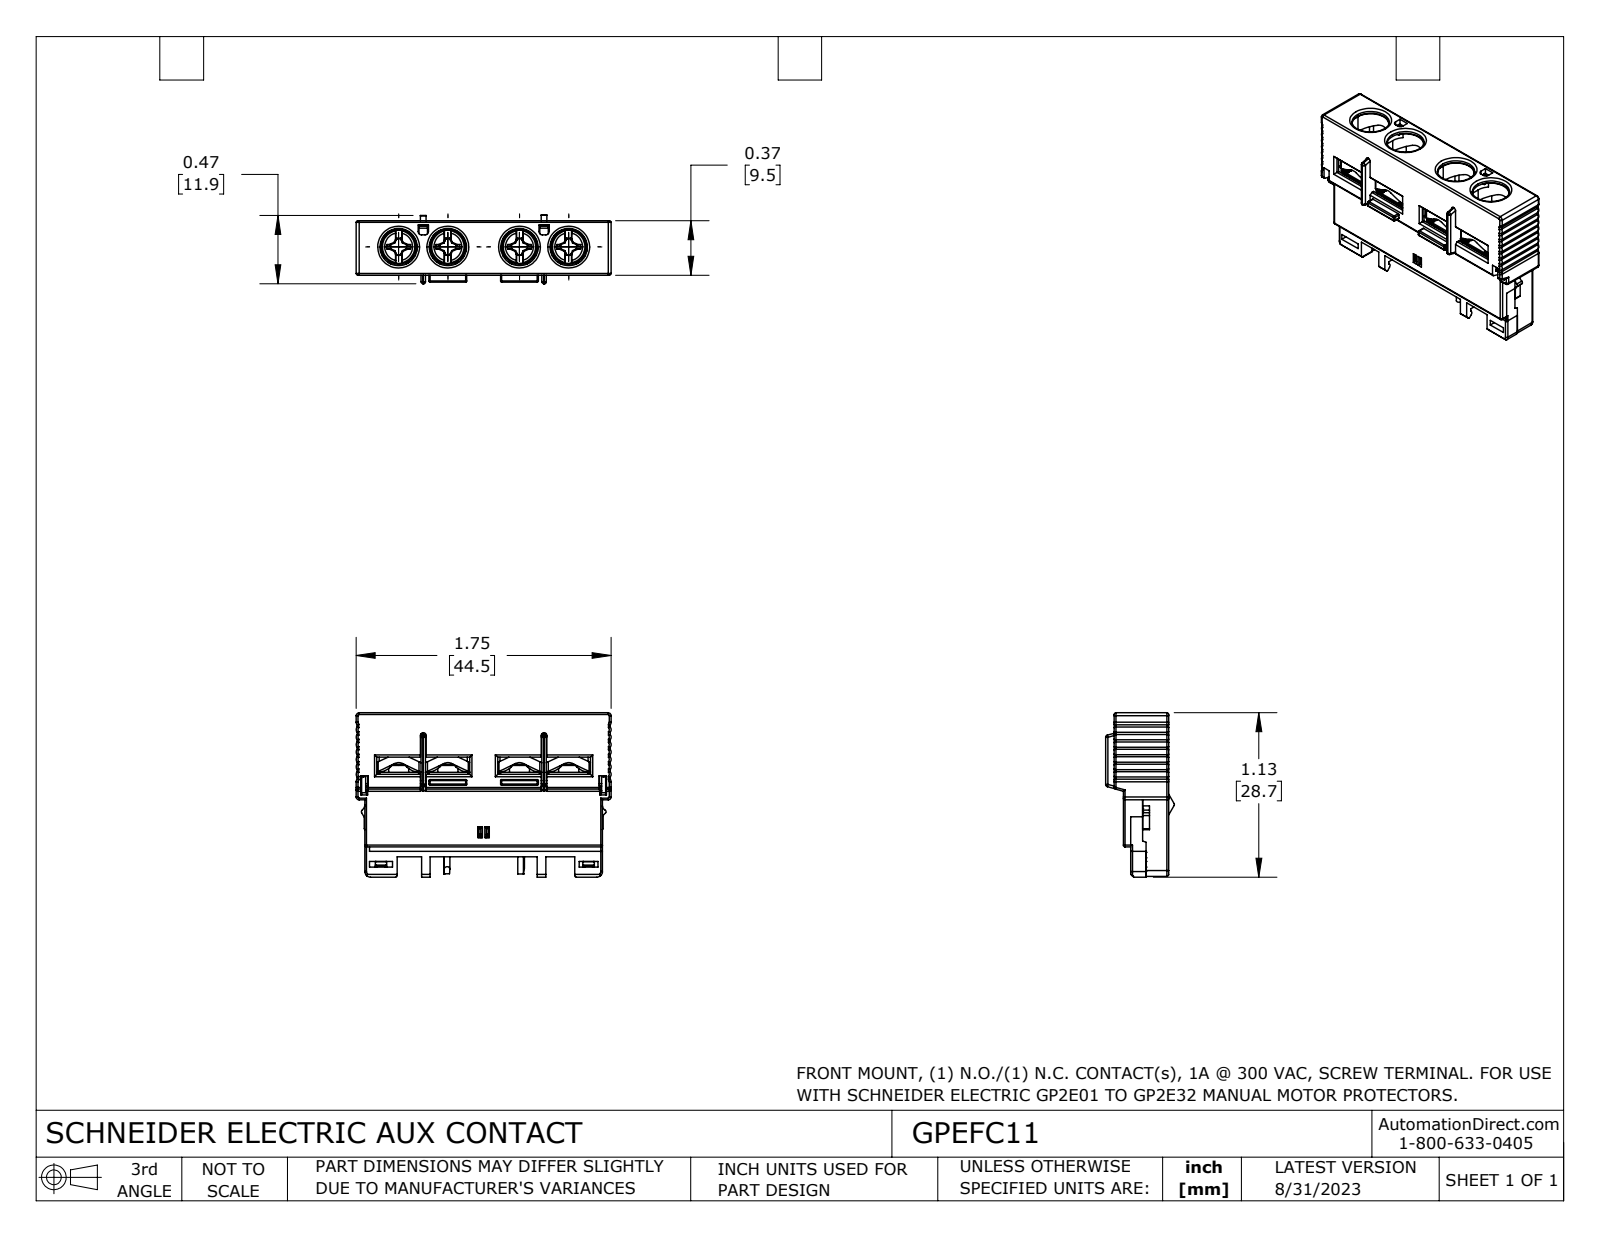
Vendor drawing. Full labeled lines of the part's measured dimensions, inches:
Part name (STEP PRODUCT): GPEFC11
STEP written by: SolidWorks 2021 (CONFIG_CONTROL_DESIGN)
Units: inches
Bodies: 16 solids, 2752 faces (1758 planar, 658 cylindrical, 336 other)
Overall size (bounding box): 1.752 × 1.13 × 0.472
Volume: 0.373 in³ · Surface area: 19.57 in²
Round holes (diameter × count): ⌀0.142 ×4, ⌀0.256 ×4
Round bosses / shafts (diameter × count): ⌀0.138 ×4, ⌀0.108 ×4, ⌀0.118 ×2
Partial cylindrical surfaces — rounded edges, fillets, slot ends (radius × count): R0.008 ×116, R0.016 ×86, R0.02 ×82, R0.012 ×67, R0.031 ×20, R0.591 ×16, R0.016 ×14, R0.118 ×12
Main face-to-face distances: 0.031, 0.063, 0.032, 0.051, 0.031, 0.343, 0.374, 0.114, 0.311, 0.386
Hole centre spacings: 0.339, 0.831, 0.492, 1.169
